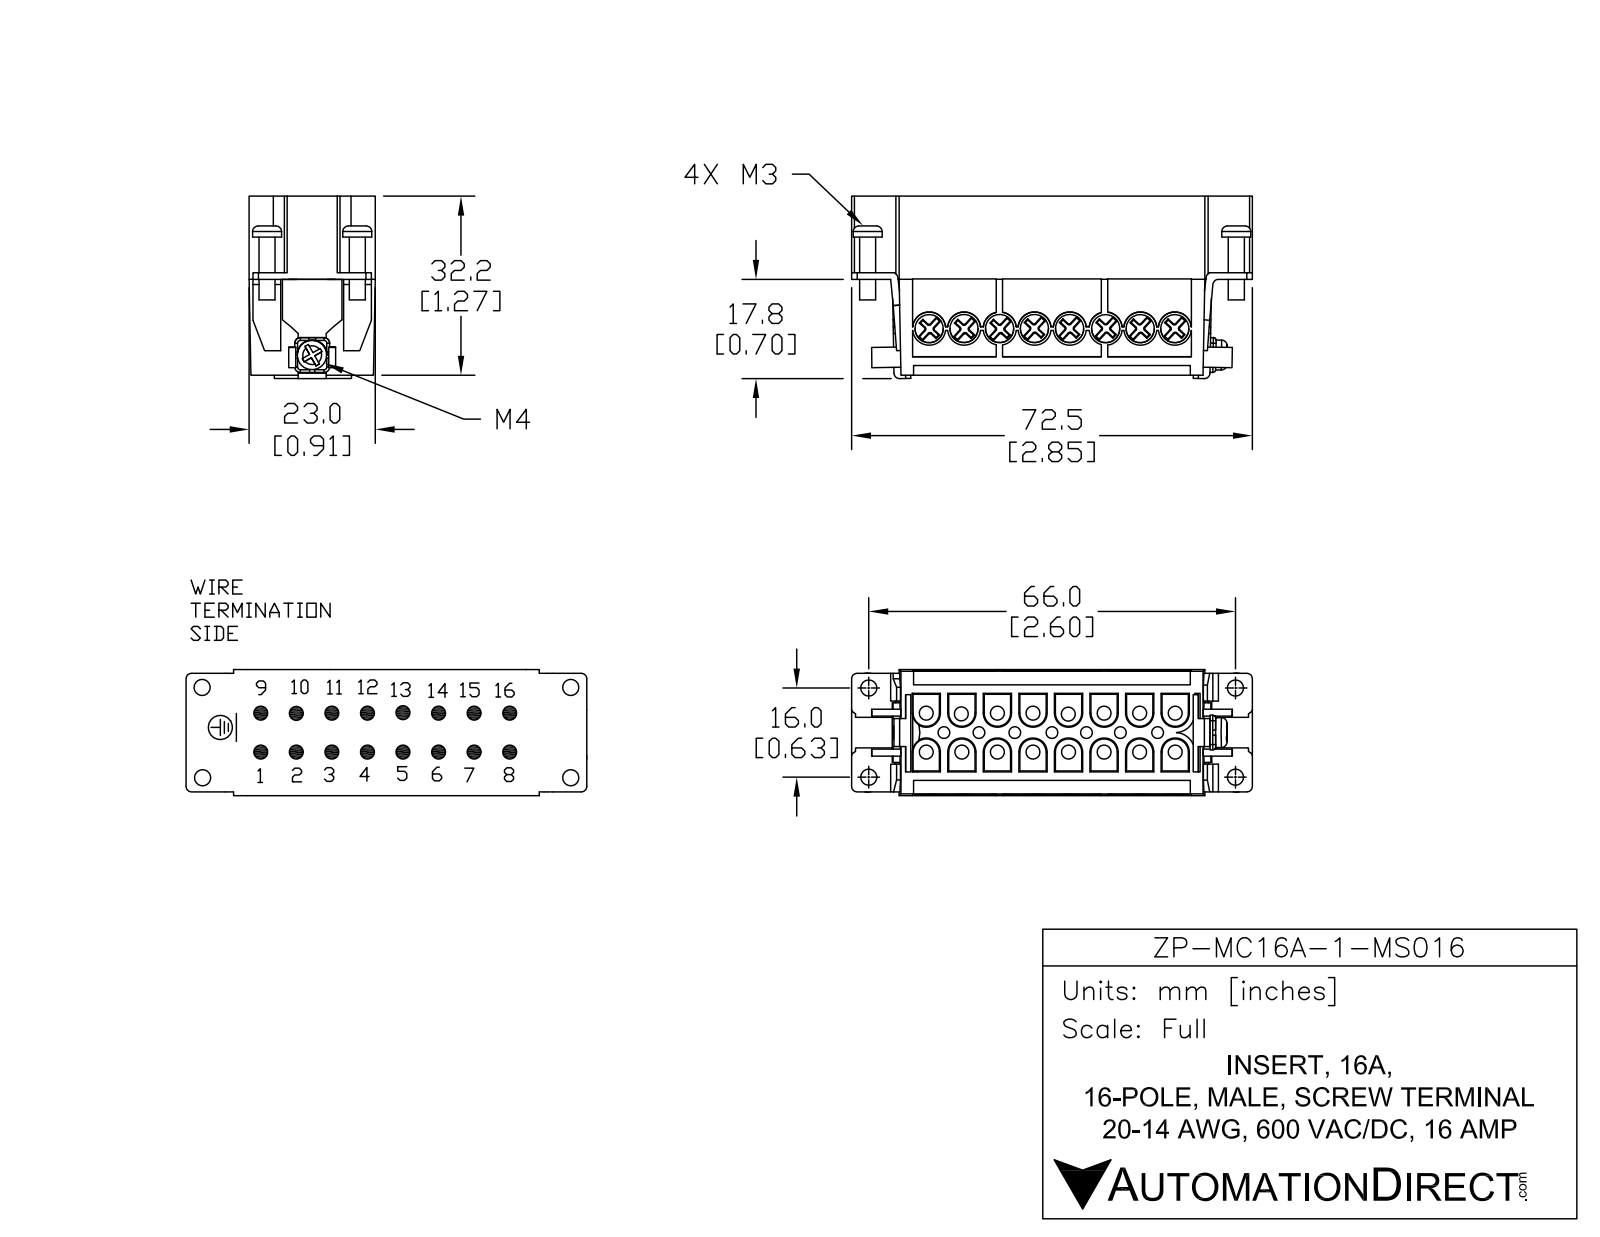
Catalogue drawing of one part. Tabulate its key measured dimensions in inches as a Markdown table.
| quantity | value |
| --- | --- |
| part name | ZP-MC16A-1-MS016 |
| STEP written by | SolidWorks 2014 (AUTOMOTIVE_DESIGN) |
| units | inches |
| bodies | 1 solid, 1016 faces (628 planar, 229 cylindrical, 159 other) |
| overall size | 2.855 × 1.272 × 0.906 |
| volume | 1.375 in³ |
| surface area | 30.9 in² |
| round holes (diameter × count) | 0.098 × 16, 0.199 × 14, 0.083 × 7, 0.199 × 2, 0.098 × 1 |
| round bosses / shafts (diameter × count) | 0.234 × 16, 0.1 × 16, 0.205 × 4, 0.114 × 4, 0.212 × 1 |
| partial cylindrical surfaces (radius × count) | 0.039 × 17, 0.02 × 12, 0.138 × 2, 0.139 × 2 |
| main face-to-face distances | 0.06, 0.846, 0.252, 0.504, 0.6, 0.906, 0.756, 0.786, 1.008, 0.394 |
| hole center spacings | 0.252, 0.373, 0.504, 0.574, 0.756, 0.805, 0.276, 1.008 |
